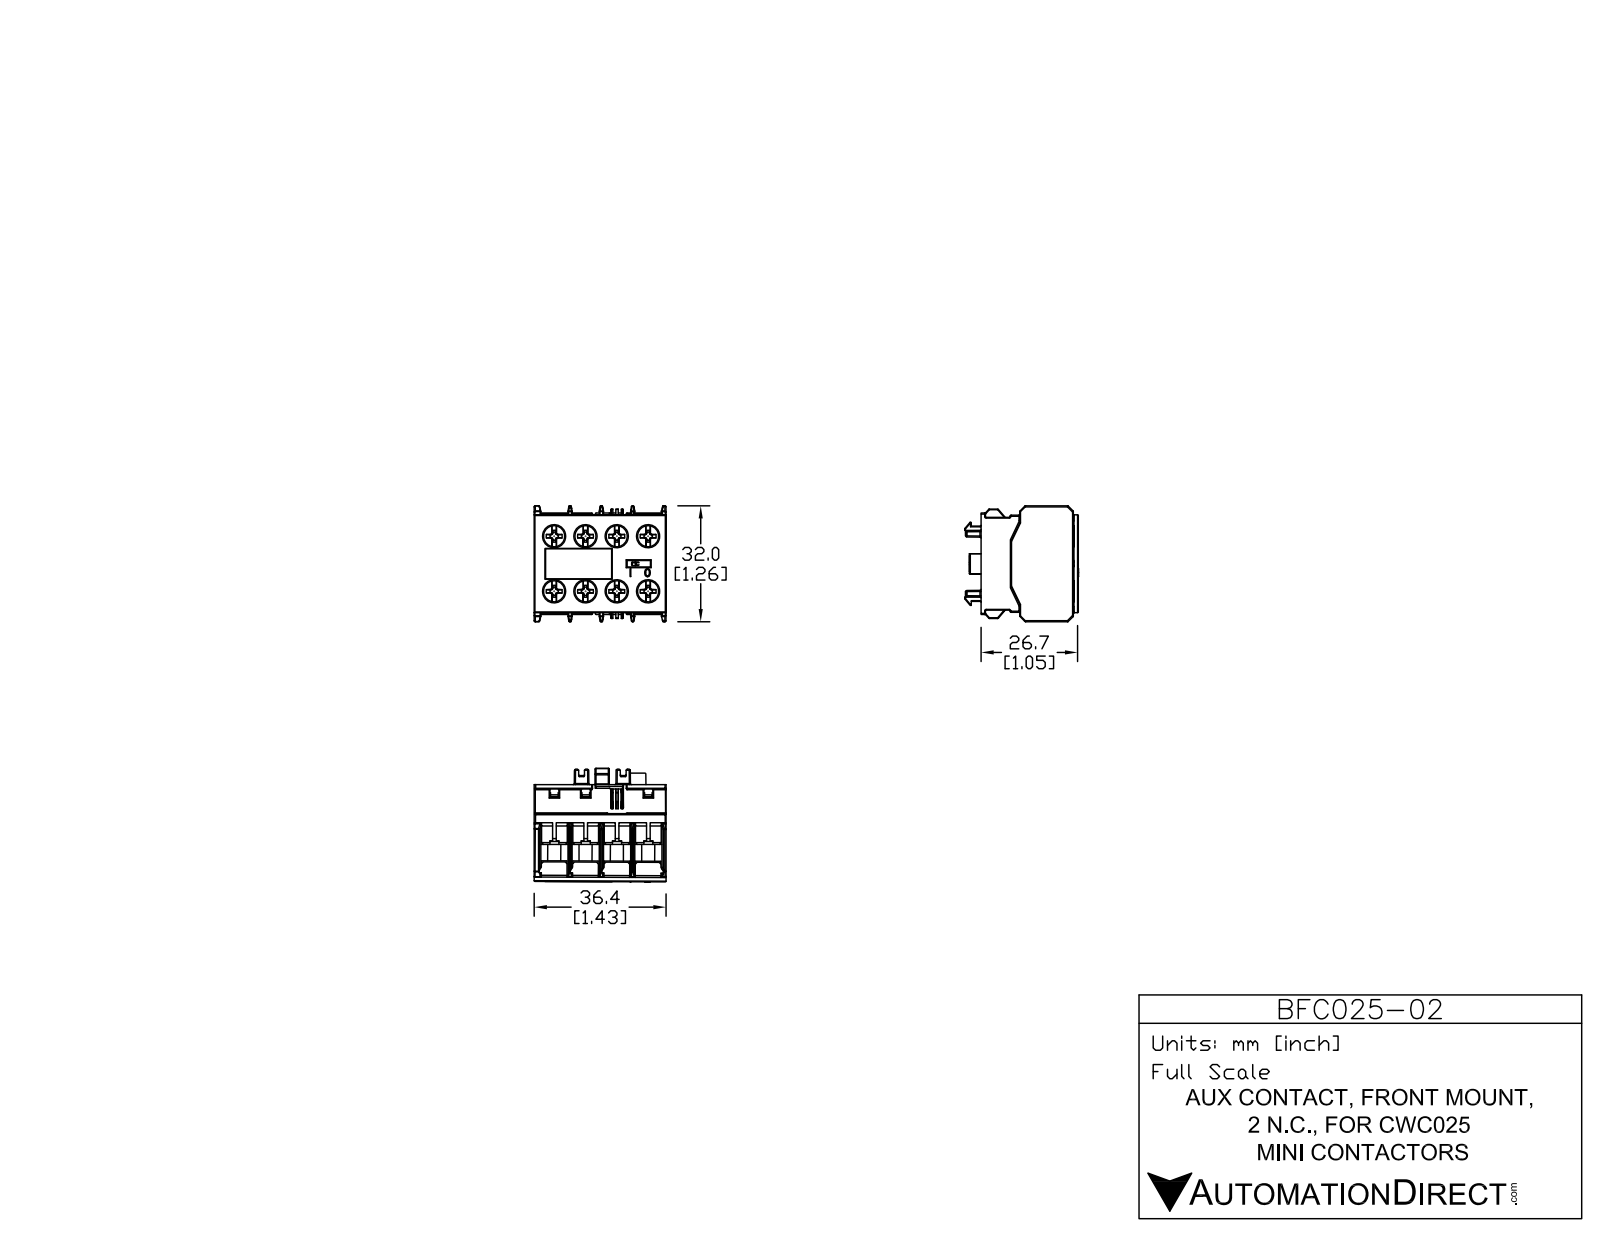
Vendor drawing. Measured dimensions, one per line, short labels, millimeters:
name: BFC025-02
written by: SolidWorks 2013 (AUTOMOTIVE_DESIGN)
unit: mm
bodies: 24 solids, 1105 faces (763 planar, 278 cylindrical, 64 other)
size: 36.5 × 32 × 31.73
volume: 26 222 mm³; area: 23 937 mm²
holes: 8× ⌀6
bosses: 8× ⌀5, 8× ⌀3
rounds: 58× R0.2, 8× R0.5, 8× R4.52, 6× R0.3, 4× R0.25, 2× R0.14, 2× R0.19
face distances: 1.25, 8.63, 17.25, 8.62, 16, 9.88, 7.38, 7.98, 25.88, 36.5
hole spacings: 8.63, 15, 17.25, 17.31, 22.86, 8.62, 17.3, 25.88
